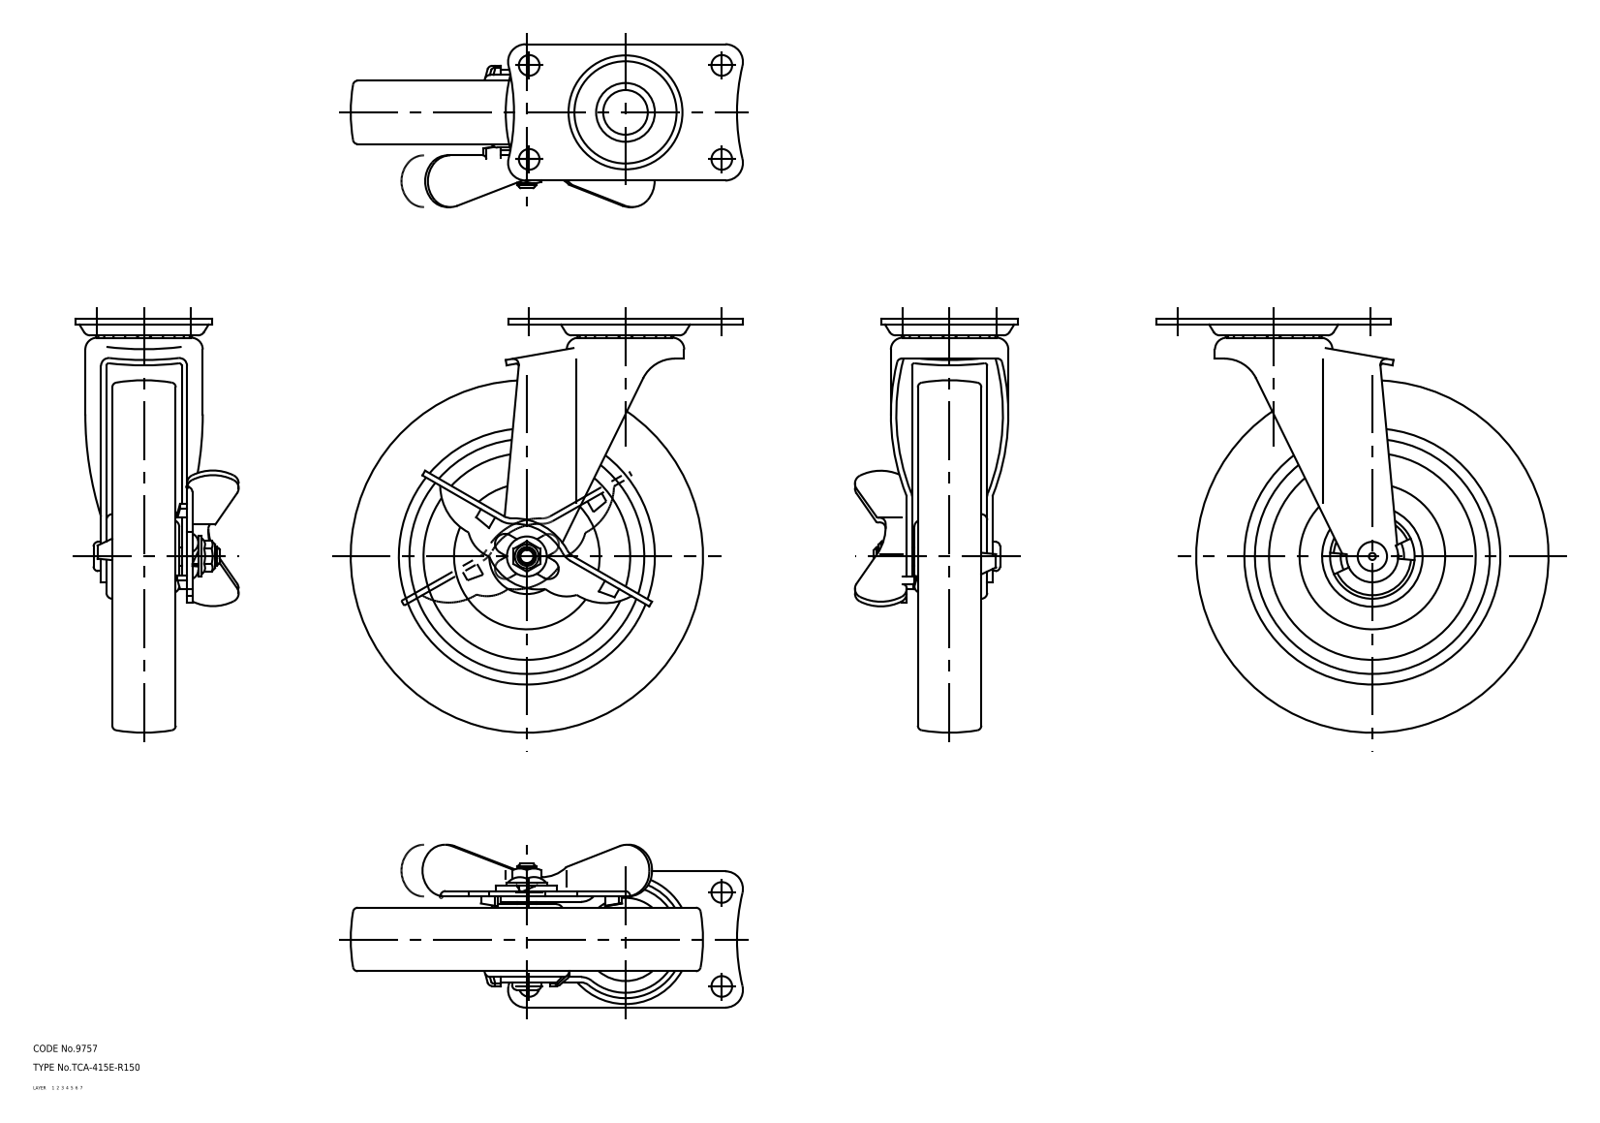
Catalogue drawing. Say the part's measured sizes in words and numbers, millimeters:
The part is named "wheel; mounting plate; main shaft; lever (+2 more)". Its 3-D file was written by "CADfix (AUTOMOTIVE_DESIGN)". It is 6 solids with 368 faces: 0 planar, 0 cylindrical and 368 other. Overall it measures 176 by 167 by 69.3 millimeters. Its volume is 520 728 cubic millimeters and its surface area 98 397 square millimeters.
